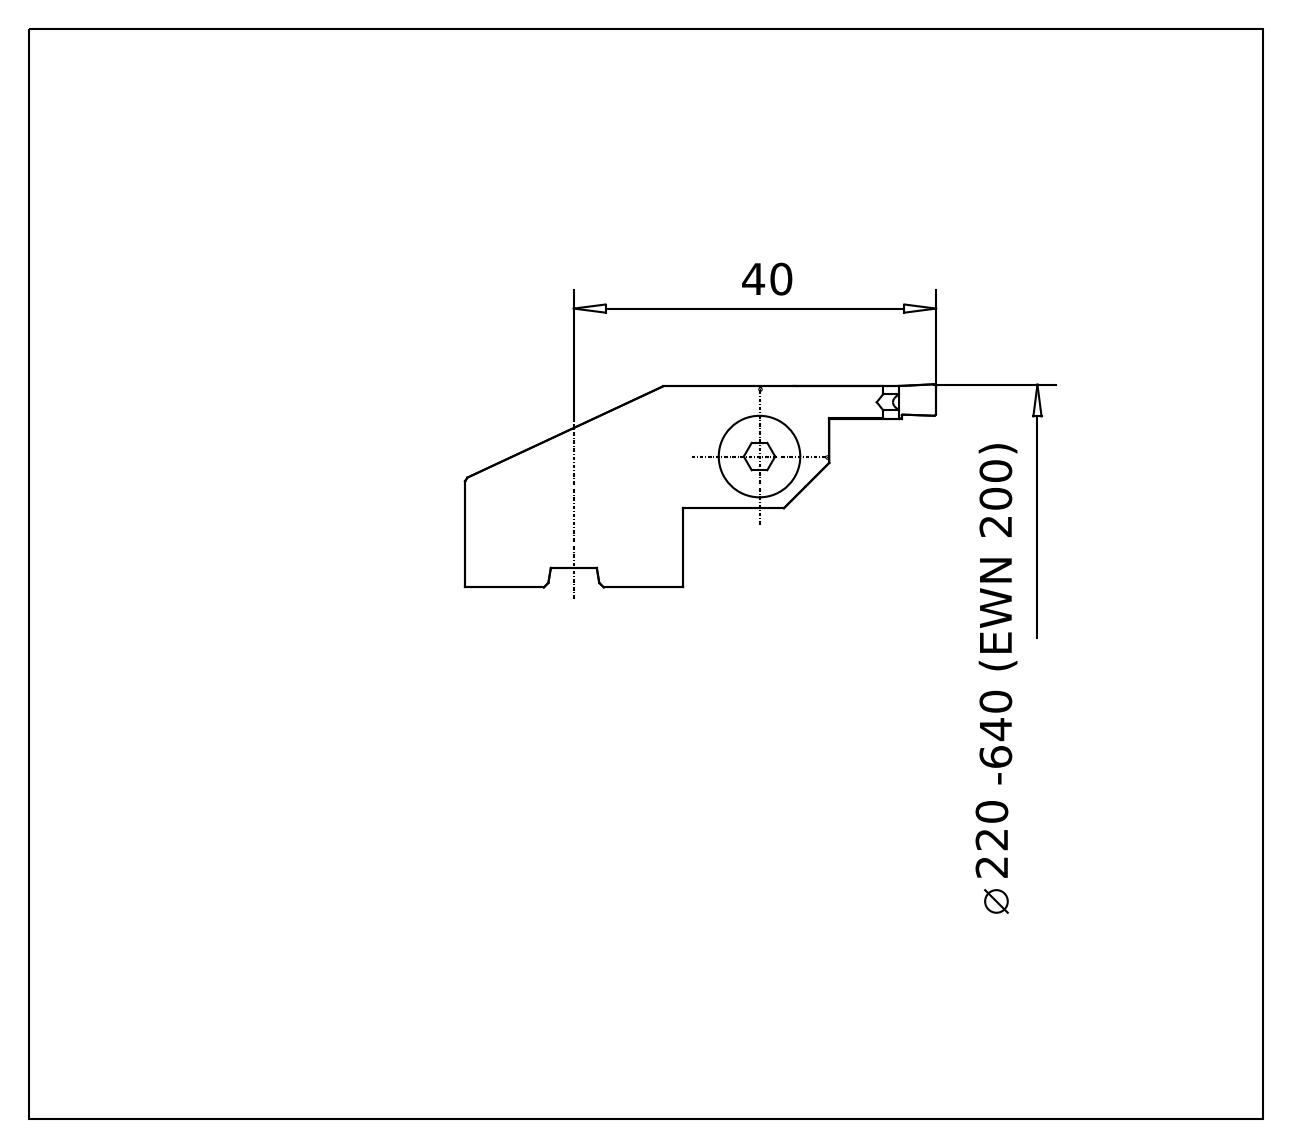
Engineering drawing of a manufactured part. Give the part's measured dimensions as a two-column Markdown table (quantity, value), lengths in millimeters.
| quantity | value |
| --- | --- |
| part name | 626.948 Kaiser ENH72 S4 220-255 R\|690.183 Kaiser ETL M5x12A;Verrundung1; 626.948 Kaiser ENH72 S4 220-255 R\|626.948 Kaiser ENH72 S4 220-255 R;Schnitt-Rotation8; 626.948 Kaiser ENH72 S4 220-255 R\|958.435 Kaiser NP4350 P20C_Einstechplatte 4mm;NONE |
| STEP written by | ACIS (automotive_design) |
| units | millimeters |
| bodies | 3 solids, 136 faces (79 planar, 39 cylindrical, 18 other) |
| overall size | 52 × 24 × 22.43 |
| volume | 10 407 mm³ |
| surface area | 5 337 mm² |
| round holes (diameter × count) | 4.2 × 1, 5.3 × 1, 6.05 × 1, 9 × 1, 11 × 1 |
| round bosses / shafts (diameter × count) | 24 × 1, 8.5 × 1, 5 × 1 |
| partial cylindrical surfaces (radius × count) | 0.2 × 4, 0.1 × 2, 1.4 × 2, 1.63 × 2, 1.26 × 1, 5 × 1, 43.5 × 1 |
| main face-to-face distances | 8.75, 12.5, 18.7, 10.9, 1.6, 4.1, 6.6, 2.15, 7.8, 6.2 |
| hole center spacings | 11.41 |
